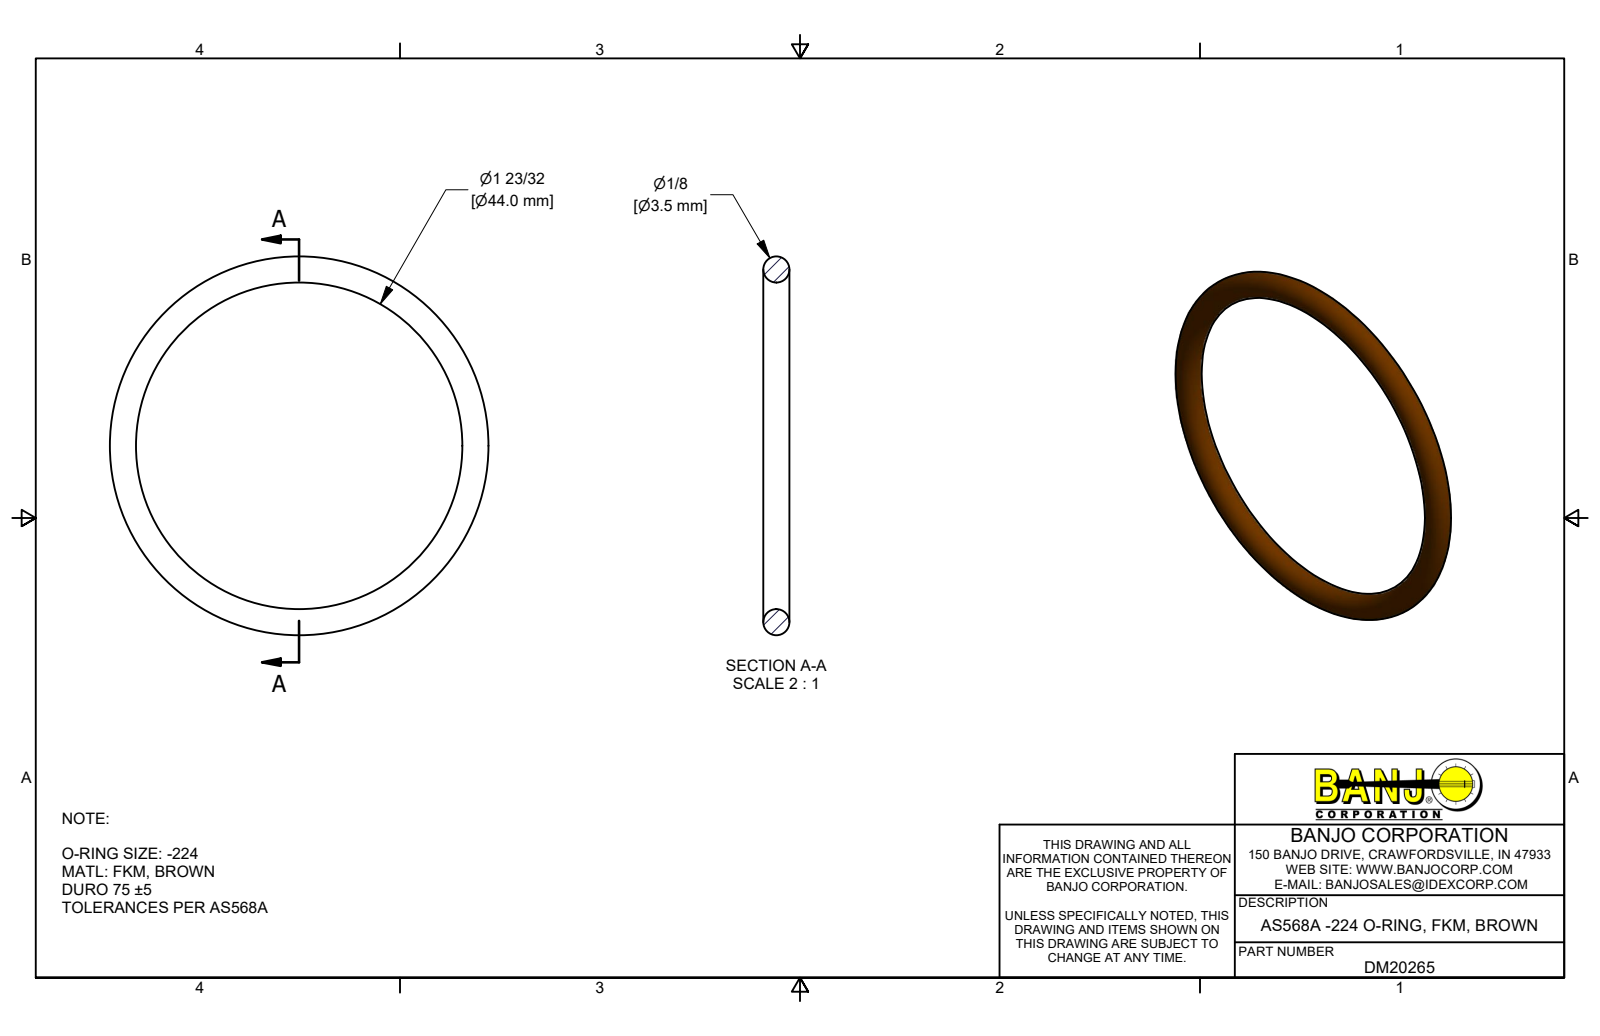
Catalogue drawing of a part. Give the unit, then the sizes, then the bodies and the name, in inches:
Units: inches
Overall size (bounding box): 2.012 × 2.012 × 0.139
Volume: 0.089 in³ · Surface area: 2.57 in²
Bodies: 1 solid, 1 faces (0 planar, 0 cylindrical, 1 other)
Part name (STEP PRODUCT): DM20265
STEP written by: Autodesk Inventor 2019 (AUTOMOTIVE_DESIGN)
